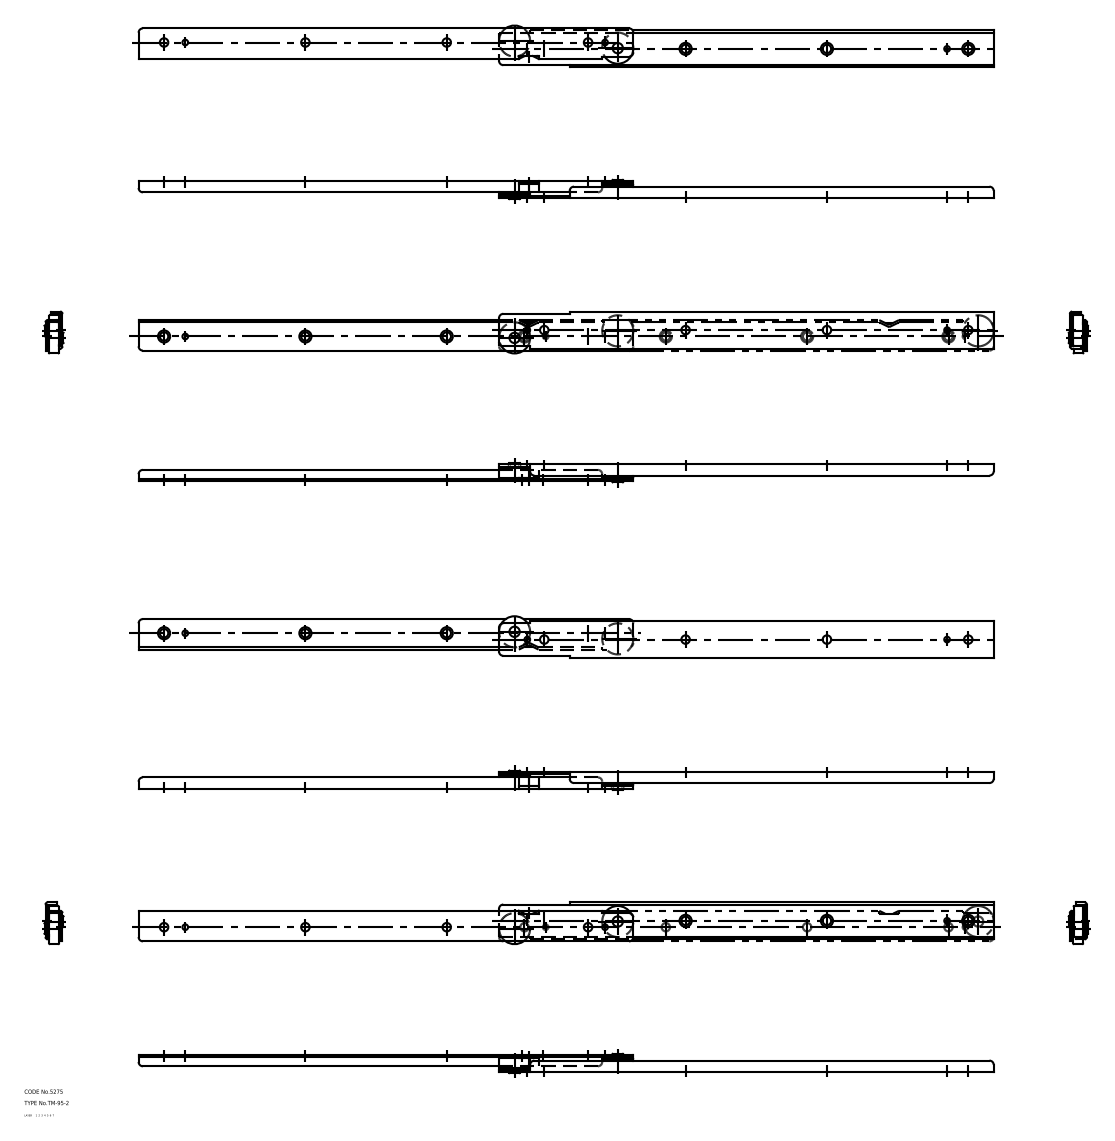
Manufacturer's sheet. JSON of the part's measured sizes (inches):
{"part_name": "roller; member_B; member_A; TM_95_2_7264_36", "step_written_by": "CADfix (AUTOMOTIVE_DESIGN)", "units": "inches", "bodies": {"solids": 4, "faces": 117, "planar": 0, "cylindrical": 0, "other": 117}, "overall_size": [23.819, 1.165, 0.528], "volume_in3": 2.477, "surface_area_in2": 76.5}
